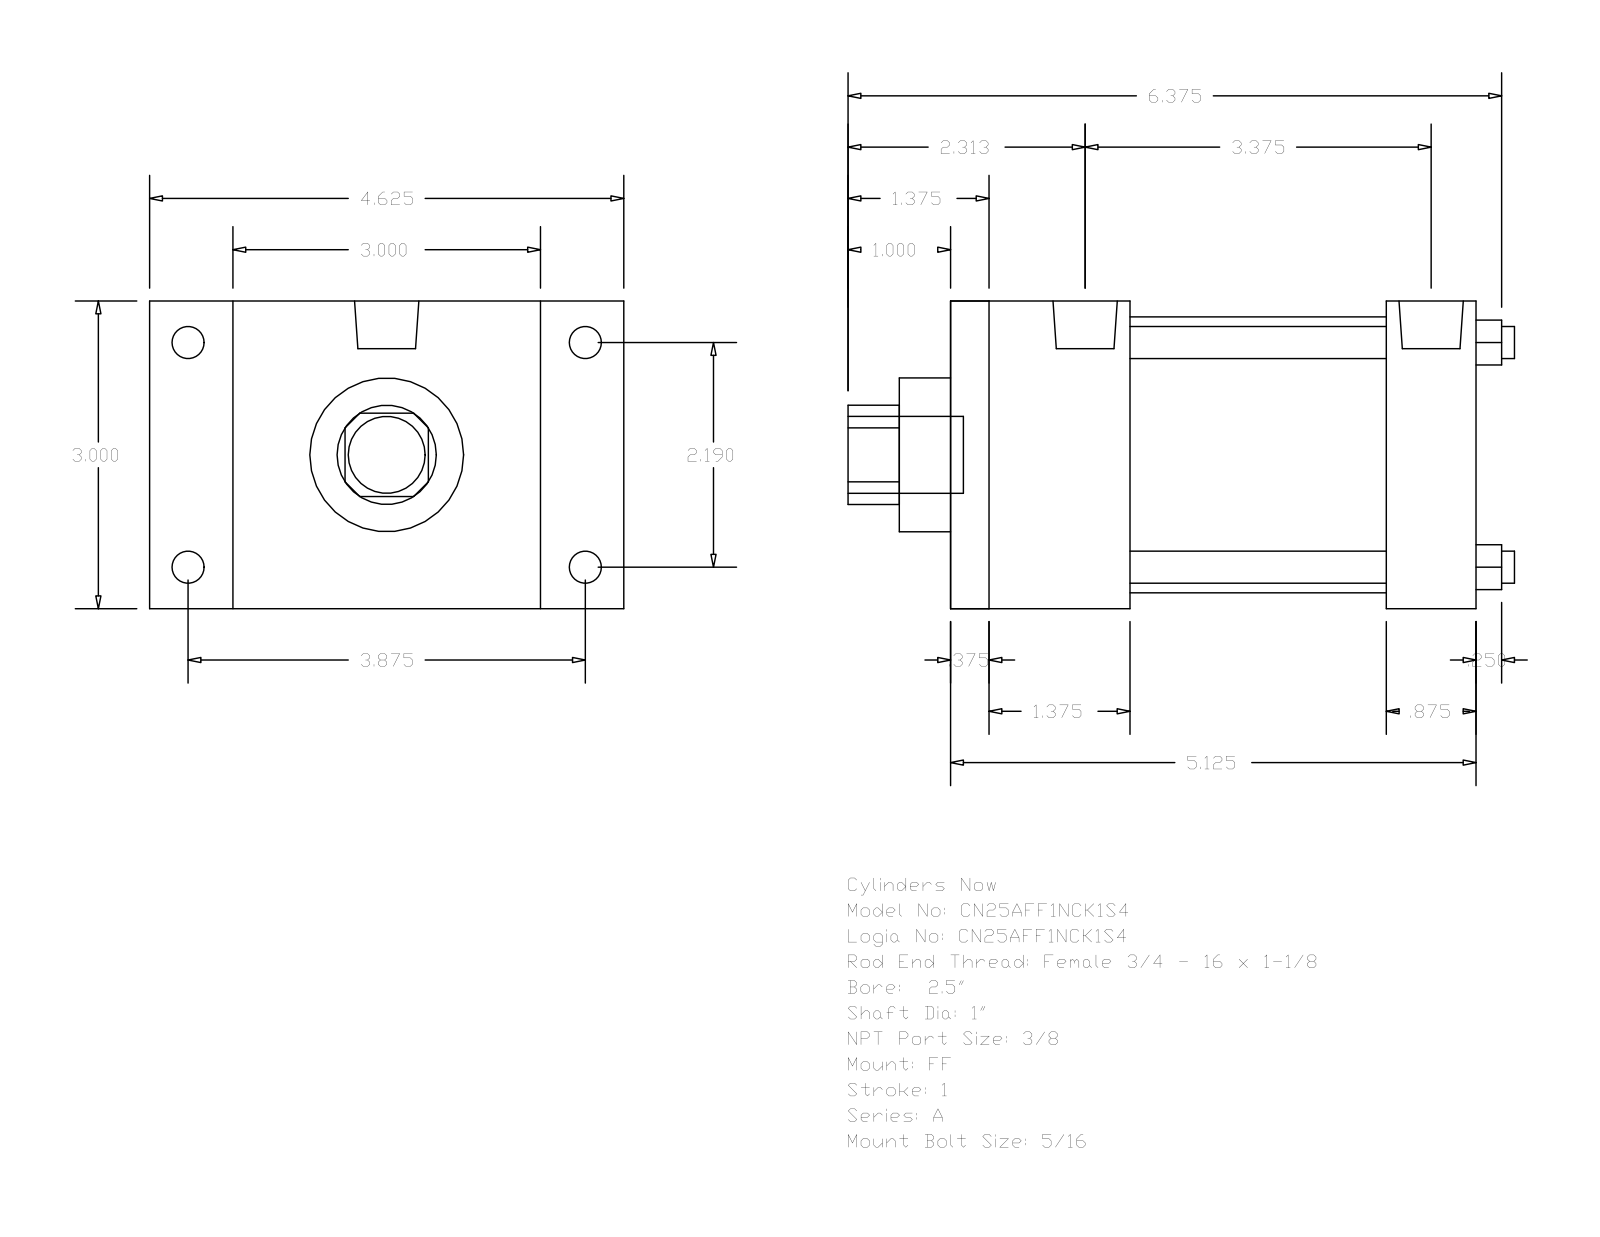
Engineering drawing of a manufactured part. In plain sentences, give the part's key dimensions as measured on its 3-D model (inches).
The part is named "A_FF__0250_1". Its 3-D file was written by "GSSL Pune (CONFIG_CONTROL_DESIGN)". It is 0 solids with 92 faces: 64 planar, 28 cylindrical and 0 other. Overall it measures 6.5 by 4.625 by 3 inches. Round holes: 4 of diameter 0.313, 1 of diameter 1, 1 of diameter 1.5, 1 of diameter 2.69. Round bosses or shafts: 4 of diameter 0.313, 4 of diameter 0.219, 2 of diameter 0.627, 1 of diameter 0.75. Partial cylindrical surfaces (rounded edges, fillets, slot ends): 1 of radius 0.484. The main face-to-face distances are 3, 5.125, 4.75, 0.375, 0.875, 1.75, 4.25, 1.375, 3.875, 2.5. The hole center spacings are 1.548, 2.19, 3.097.
